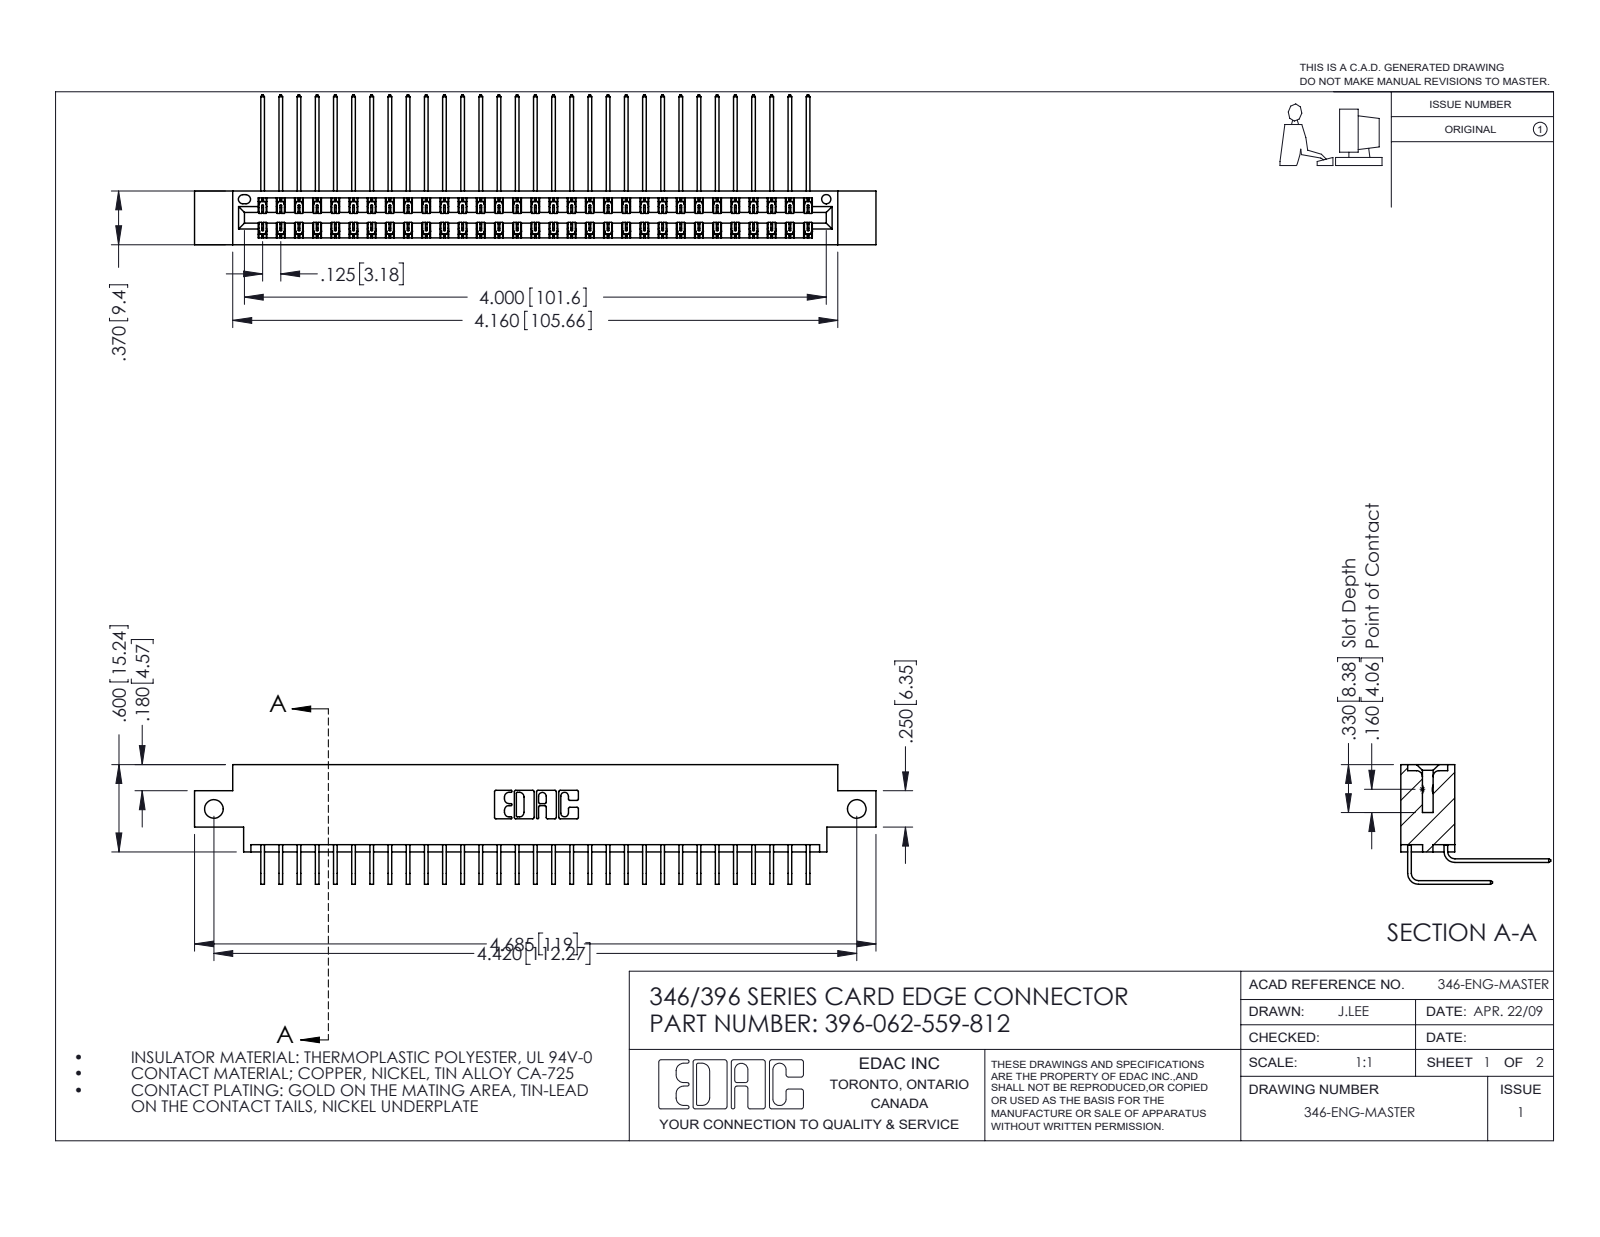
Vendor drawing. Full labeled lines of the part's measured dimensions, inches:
Part name (STEP PRODUCT): 346 Part_0.170 Offset - Side Mount; 345-292-001_559 Tail - 2; 345-292-001_558 559 Tail - 1; 396-062-559-812
STEP written by: SolidWorks 2016 (CONFIG_CONTROL_DESIGN)
Units: inches
Bodies: 63 solids, 3474 faces (2374 planar, 1100 cylindrical, 0 other)
Overall size (bounding box): 4.685 × 1.03 × 0.823
Volume: 0.71 in³ · Surface area: 27.24 in²
Round holes (diameter × count): ⌀0.128 ×2, ⌀0.064 ×1
Partial cylindrical surfaces — rounded edges, fillets, slot ends (radius × count): R0.006 ×93, R0.01 ×22, R0.007 ×6, R0.031 ×6, R0.026 ×3, R0.014 ×2, R0.022 ×2, R0.024 ×2
Main face-to-face distances: 0.048, 0.322, 0.025, 0.37, 0.25, 0.072, 0.298, 0.275, 0.148, 0.222
Hole centre spacings: 4.42
